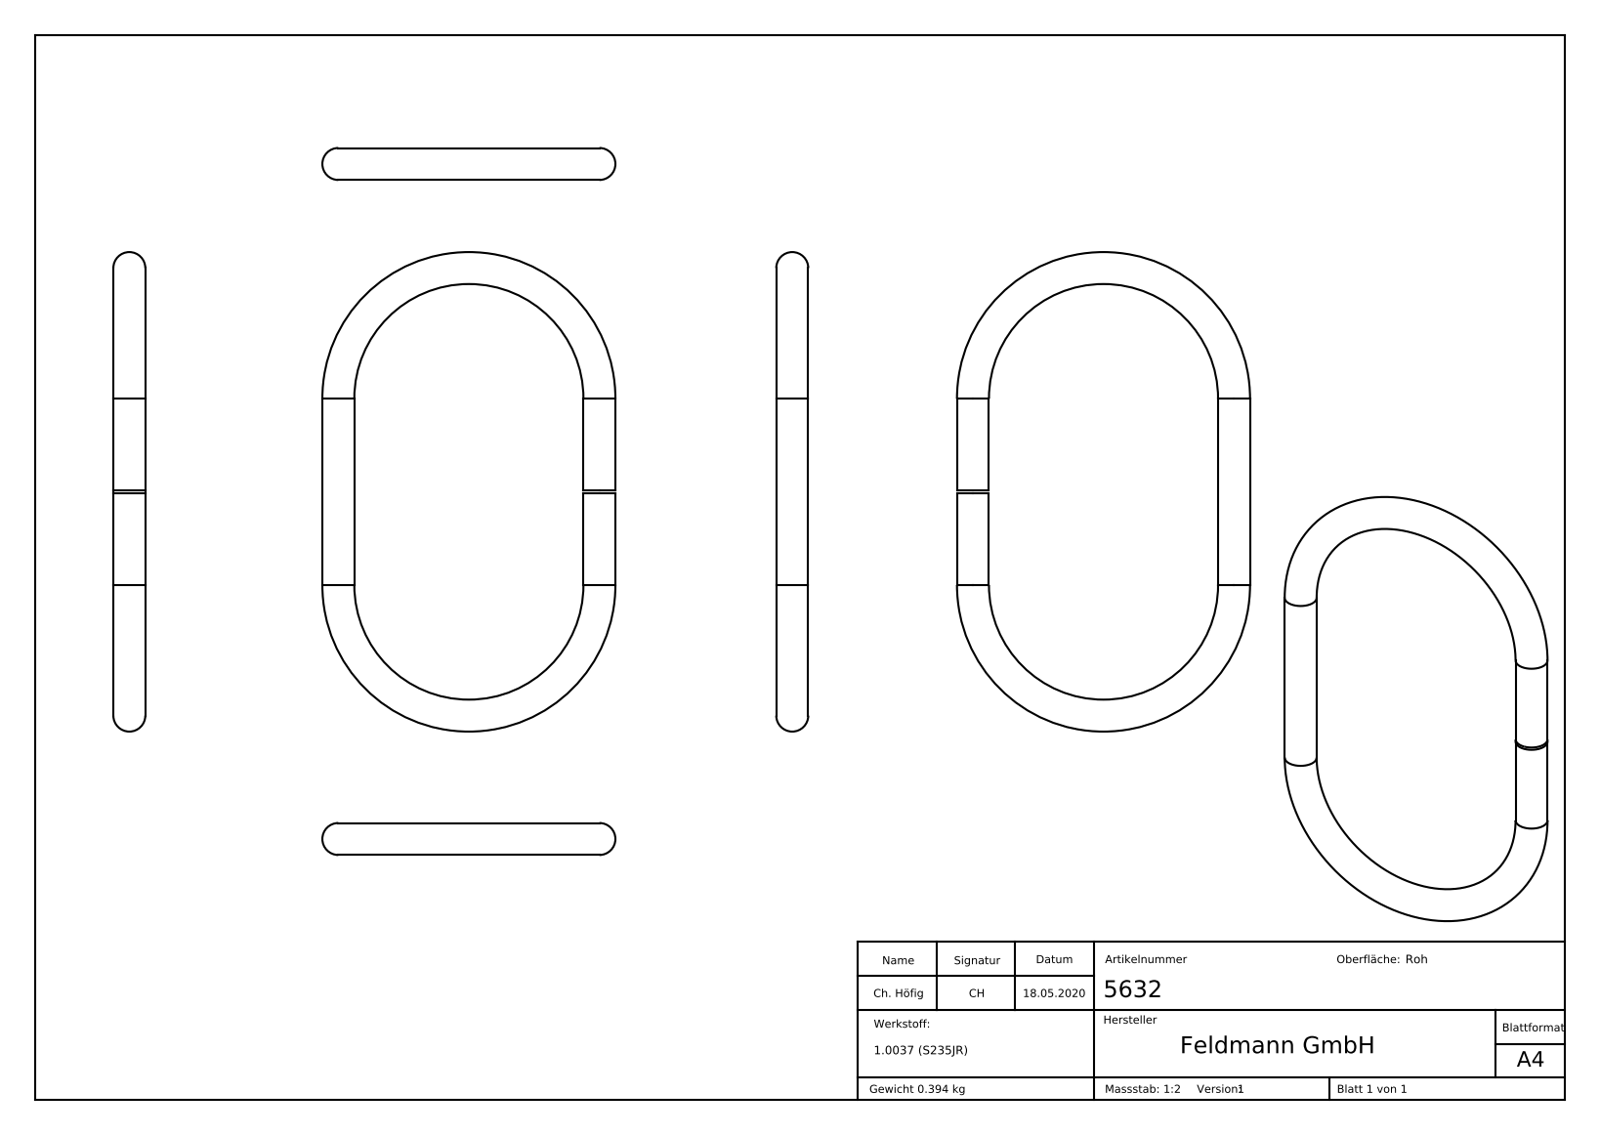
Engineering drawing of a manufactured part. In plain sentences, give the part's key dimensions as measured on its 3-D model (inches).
The part is named "5632". Its 3-D file was written by "SolidWorks 2015 (CONFIG_CONTROL_DESIGN)". It is 1 solid with 180 faces: 90 planar, 3 cylindrical and 87 other. Overall it measures 7.087 by 4.331 by 0.472 inches. Its volume is 3.084 cubic inches and its surface area 26.47 square inches. Round bosses or shafts: 2 of diameter 0.472. The main face-to-face distances are 0.039, 0.043, 0.07, 0.026, 0.033, 0.017, 0.039, 0.048, 0.03, 0.031.
